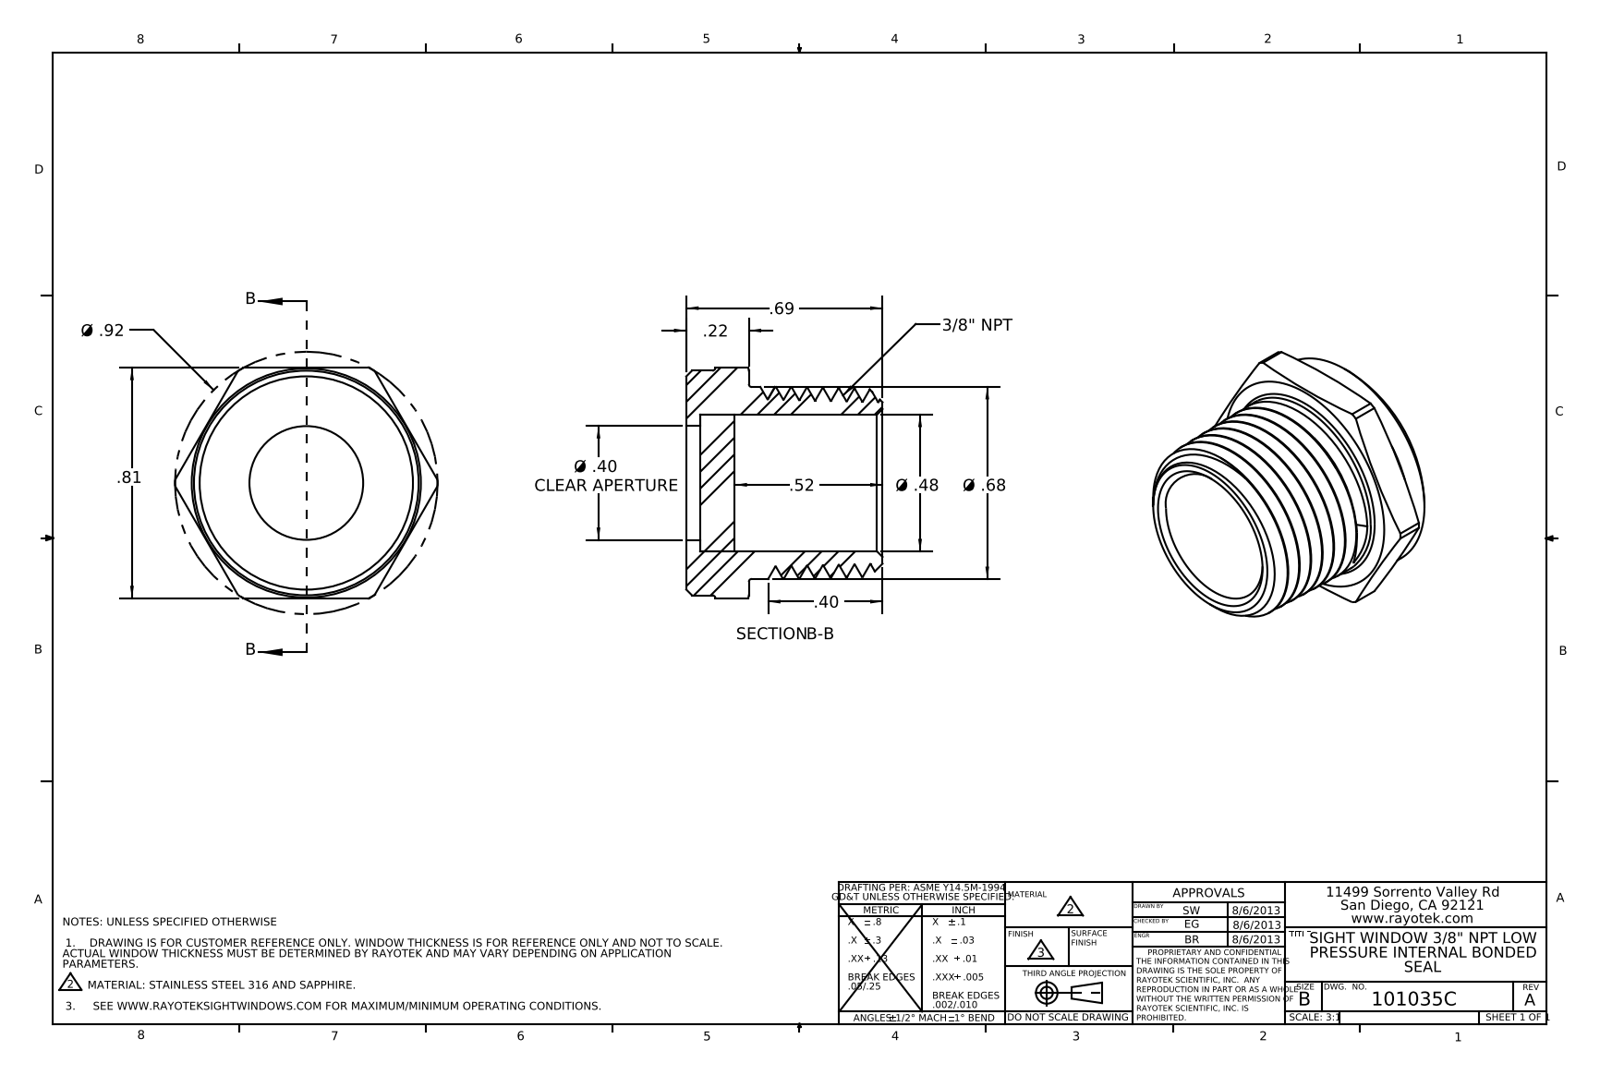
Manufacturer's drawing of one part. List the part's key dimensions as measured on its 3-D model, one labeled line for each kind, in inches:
Part name (STEP PRODUCT): 403035
STEP written by: SolidWorks 2012 (AUTOMOTIVE_DESIGN)
Units: inches
Bodies: 2 solids, 64 faces (15 planar, 18 cylindrical, 31 other)
Overall size (bounding box): 0.923 × 0.81 × 0.69
Volume: 0.161 in³ · Surface area: 4.483 in²
Round holes (diameter × count): ⌀0.4 ×1, ⌀0.48 ×1
Round bosses / shafts (diameter × count): ⌀0.79 ×1, ⌀0.675 ×1
Partial cylindrical surfaces — rounded edges, fillets, slot ends (radius × count): R0.462 ×1
Main face-to-face distances: 0.05, 0.17, 0.12, 0.81, 0.22, 0.69, 0.64, 0.52, 0.47
